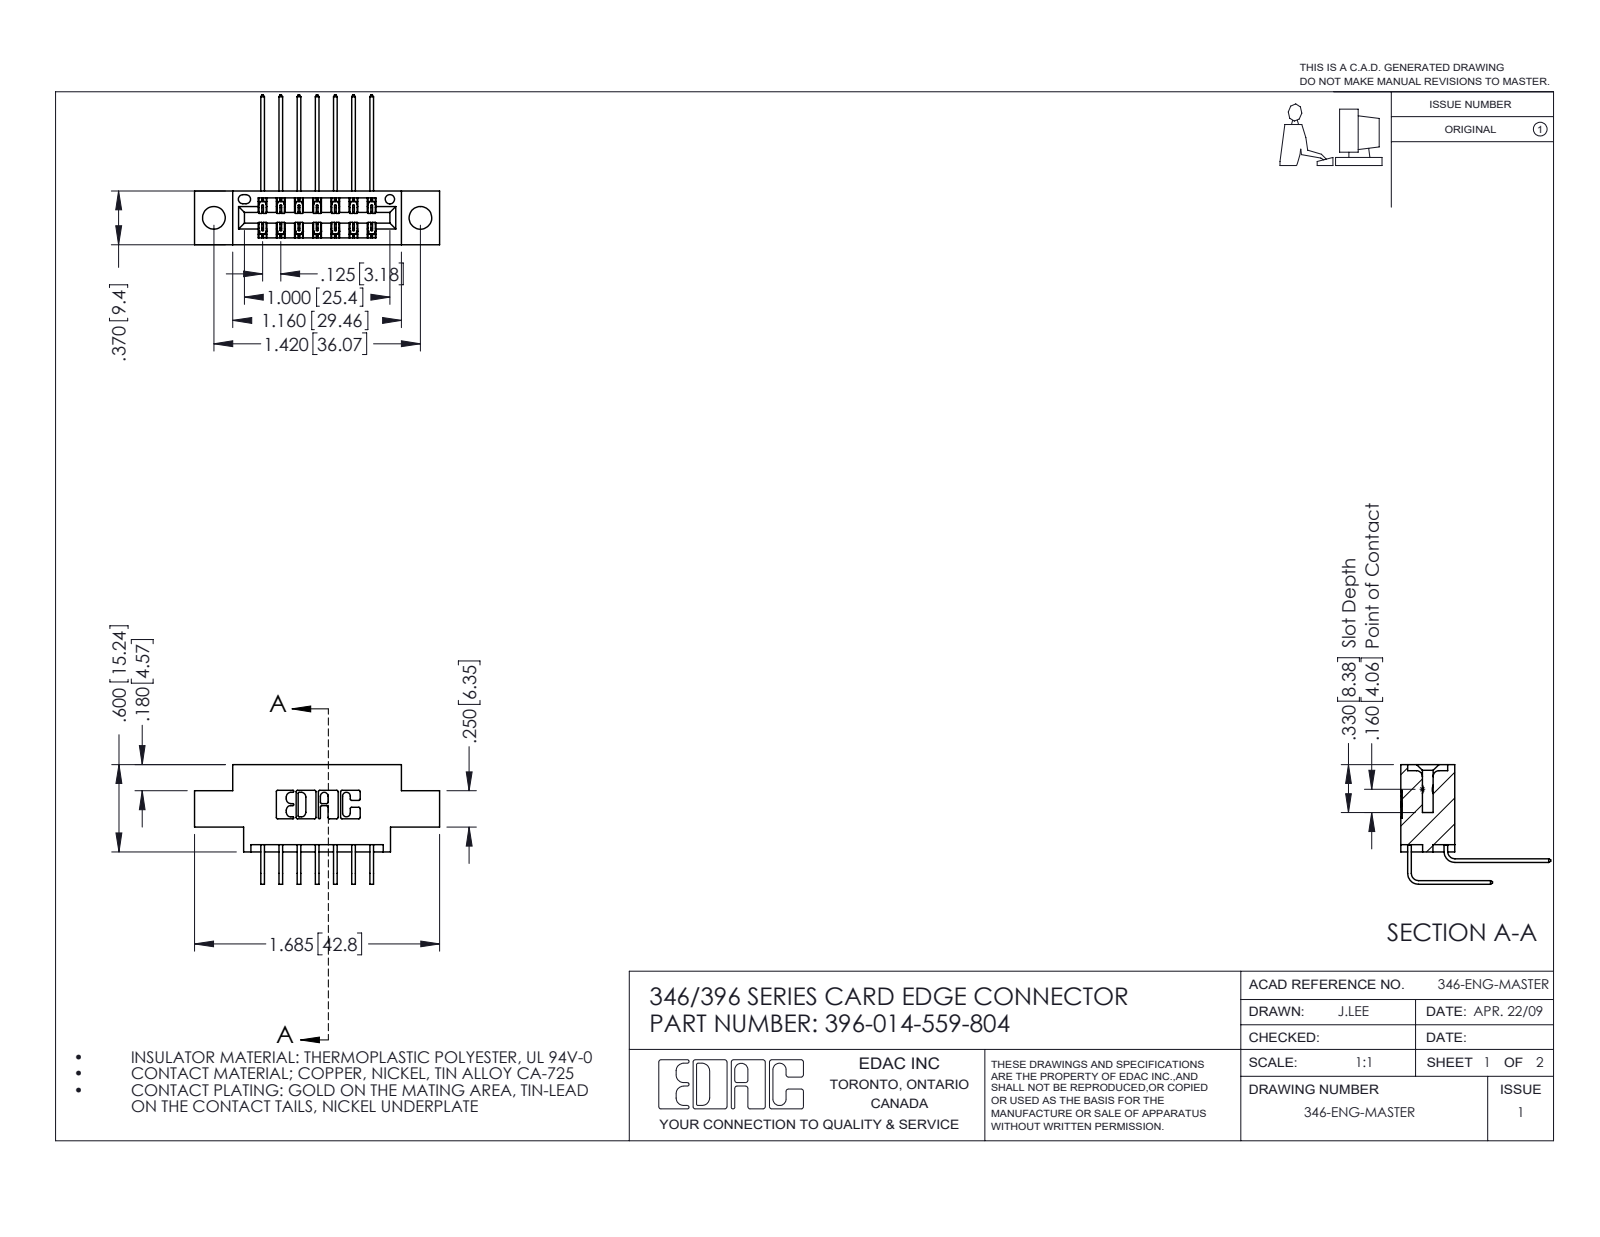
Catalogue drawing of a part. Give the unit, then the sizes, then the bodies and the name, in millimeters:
Units: millimetres
Overall size (bounding box): 42.8 × 26.2 × 20.9
Round holes (diameter × count): ⌀4 ×2, ⌀1.6 ×1
Partial cylindrical surfaces — rounded edges, fillets, slot ends (radius × count): R0.3 ×22, R0.2 ×21, R0.2 ×6, R0.8 ×6, R0.7 ×3, R0.4 ×2, R0.6 ×2, R0.6 ×2
Main face-to-face distances: 6.4, 9.4, 1.2, 8.2, 0.6, 1.8, 3.2, 7.6, 3.8, 5.6
Hole centre spacings: 6.2, 30.9, 36.1
Volume: 3 740 mm³ · Surface area: 4 971 mm²
Bodies: 15 solids, 882 faces (598 planar, 284 cylindrical, 0 other)
Part name (STEP PRODUCT): 346 Part_0.170 Offset - 0.156 Dia-TH; 396-014-559-804; 345-292-001_558 559 Tail - 1; 345-292-001_559 Tail - 2
STEP written by: SolidWorks 2016 (CONFIG_CONTROL_DESIGN)
